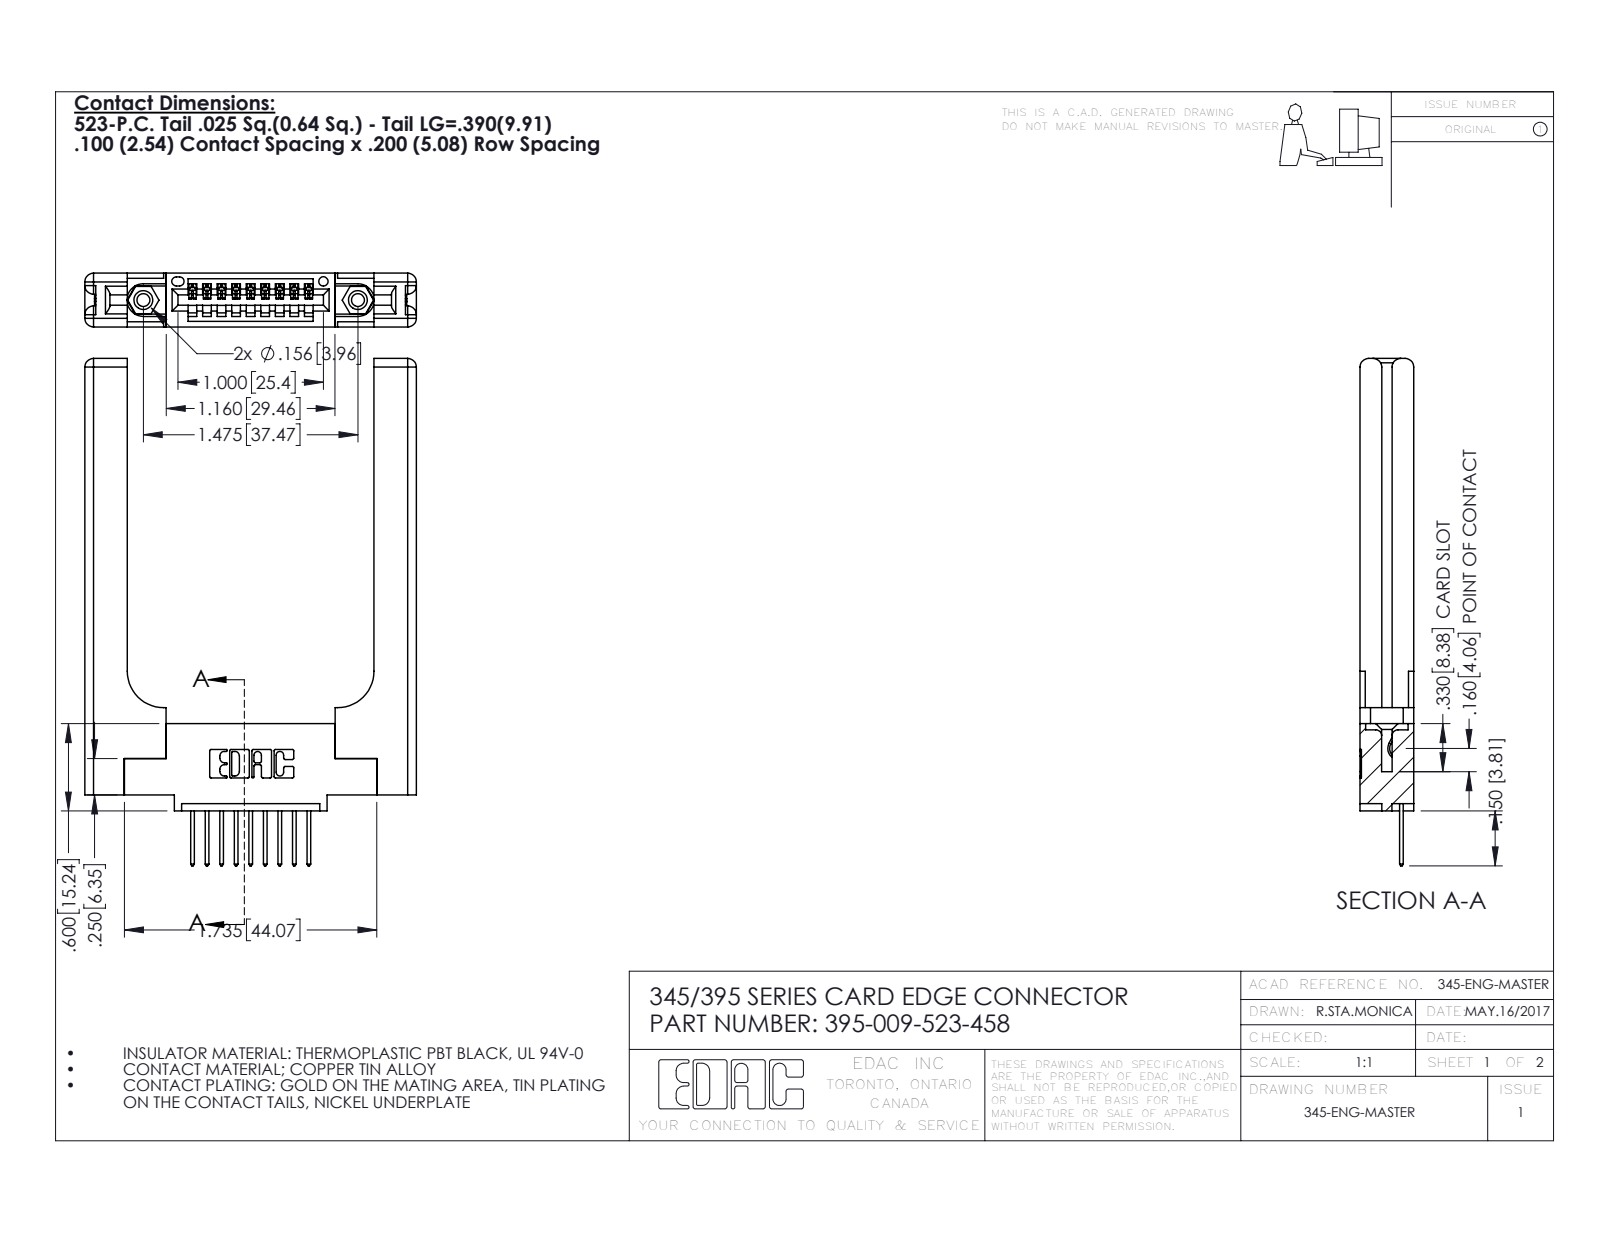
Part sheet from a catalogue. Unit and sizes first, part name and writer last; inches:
Units: inches
Overall size (bounding box): 3.487 × 2.279 × 0.37
Round holes (diameter × count): ⌀0.089 ×2, ⌀0.125 ×2, ⌀0.156 ×2, ⌀0.064 ×1
Round bosses / shafts (diameter × count): ⌀0.155 ×2
Partial cylindrical surfaces — rounded edges, fillets, slot ends (radius × count): R0.01 ×22, R0.006 ×18, R0.01 ×18, R0.06 ×16, R0.007 ×6, R0.031 ×6, R0.026 ×3, R0.03 ×2
Main face-to-face distances: 0.37, 0.15, 0.072, 0.22, 0.077, 0.148, 0.298, 1.696, 0.071, 0.292
Hole centre spacings: 0.27, 1.244, 1.475
Volume: 0.833 in³ · Surface area: 18.28 in²
Bodies: 14 solids, 908 faces (592 planar, 256 cylindrical, 60 other)
Part name (STEP PRODUCT): 395-009-523-458; 345-292-001_345-293-123; 345-220-058_345-220-058; 345-250-001_345-250-001-102 (+1 more)
STEP written by: SolidWorks 2016 (CONFIG_CONTROL_DESIGN)
